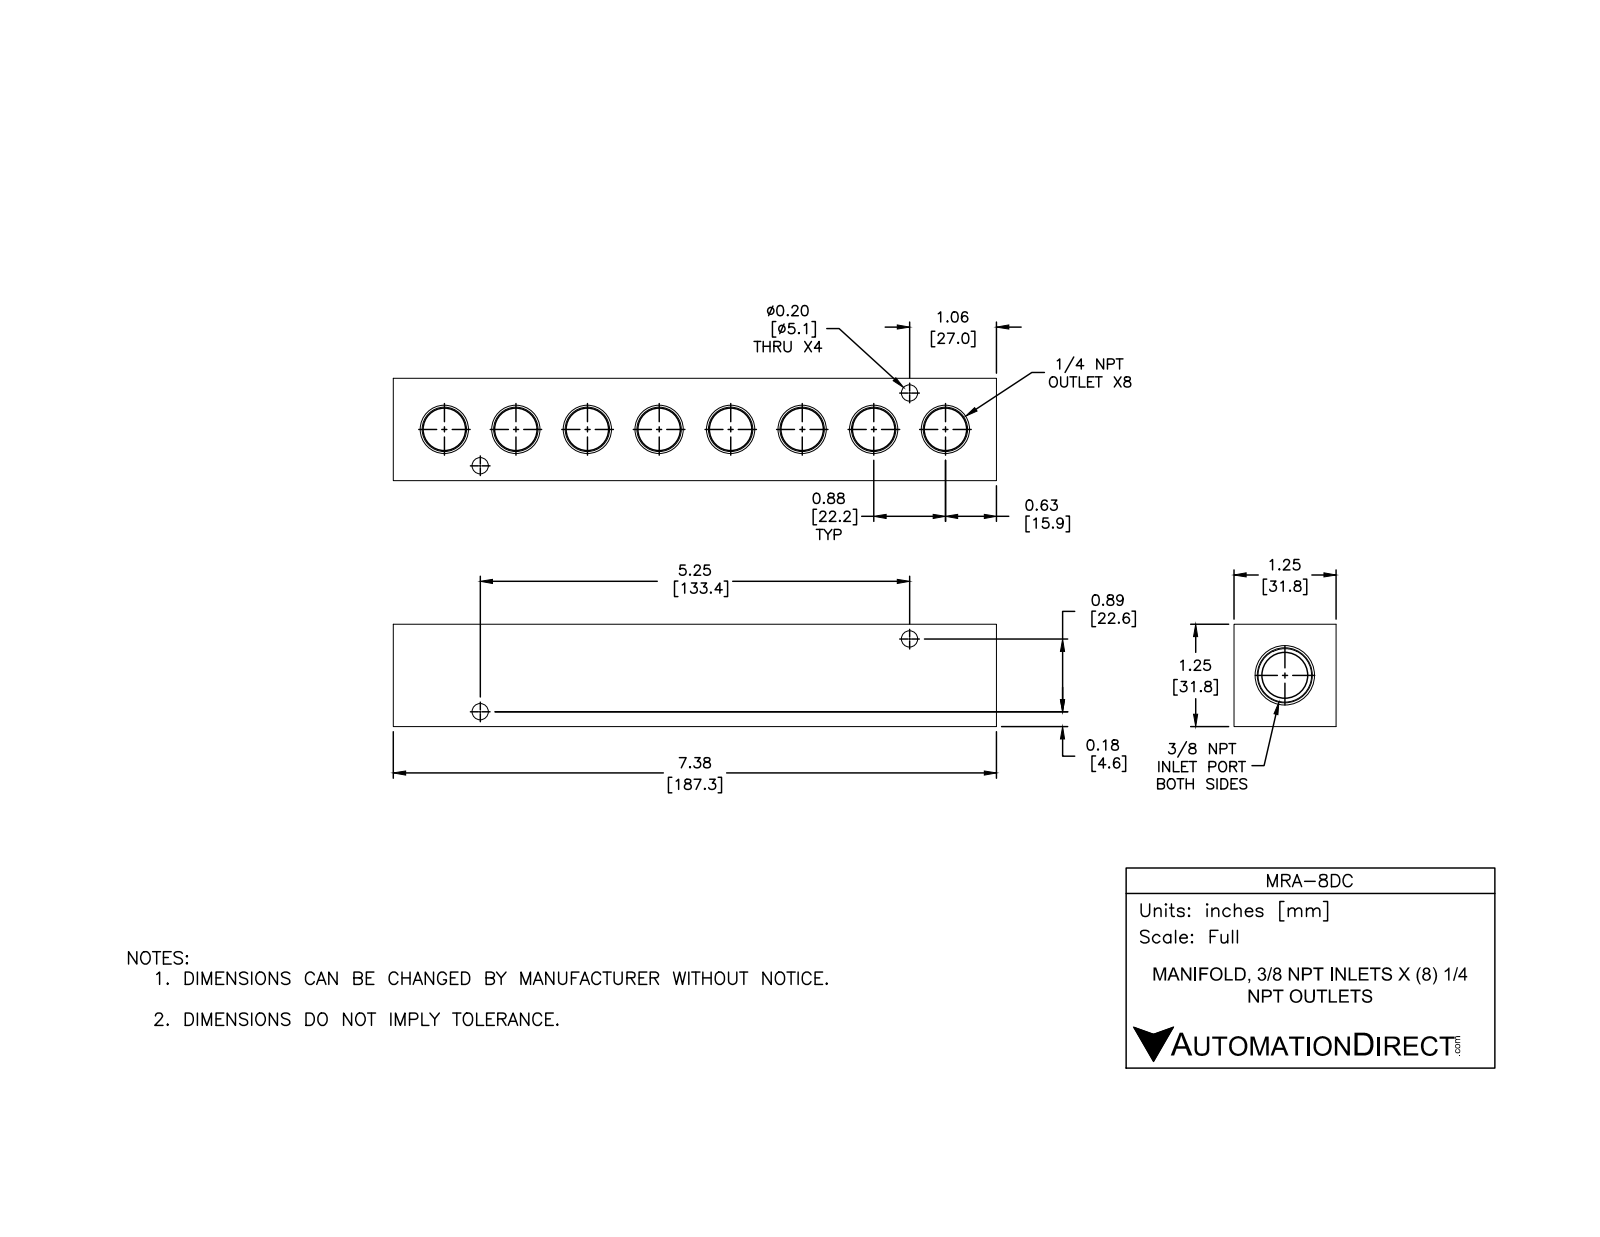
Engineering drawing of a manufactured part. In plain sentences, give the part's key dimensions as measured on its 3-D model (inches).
The part is named "MRA-8DC". Its 3-D file was written by "SolidWorks 2015 (CONFIG_CONTROL_DESIGN)". It is 1 solid with 98 faces: 24 planar, 34 cylindrical and 40 other. Overall it measures 7.375 by 1.25 by 1.25 inches. Its volume is 8.808 cubic inches and its surface area 57.11 square inches. Round holes: 4 of diameter 0.2, 1 of diameter 0.562. Partial cylindrical surfaces (rounded edges, fillets, slot ends): 8 of radius 0.219. The main face-to-face distances are 1.25, 7.375, 0.86, 0.39, 0.41, 6.965, 6.555. The hole center spacings are 5.324.
